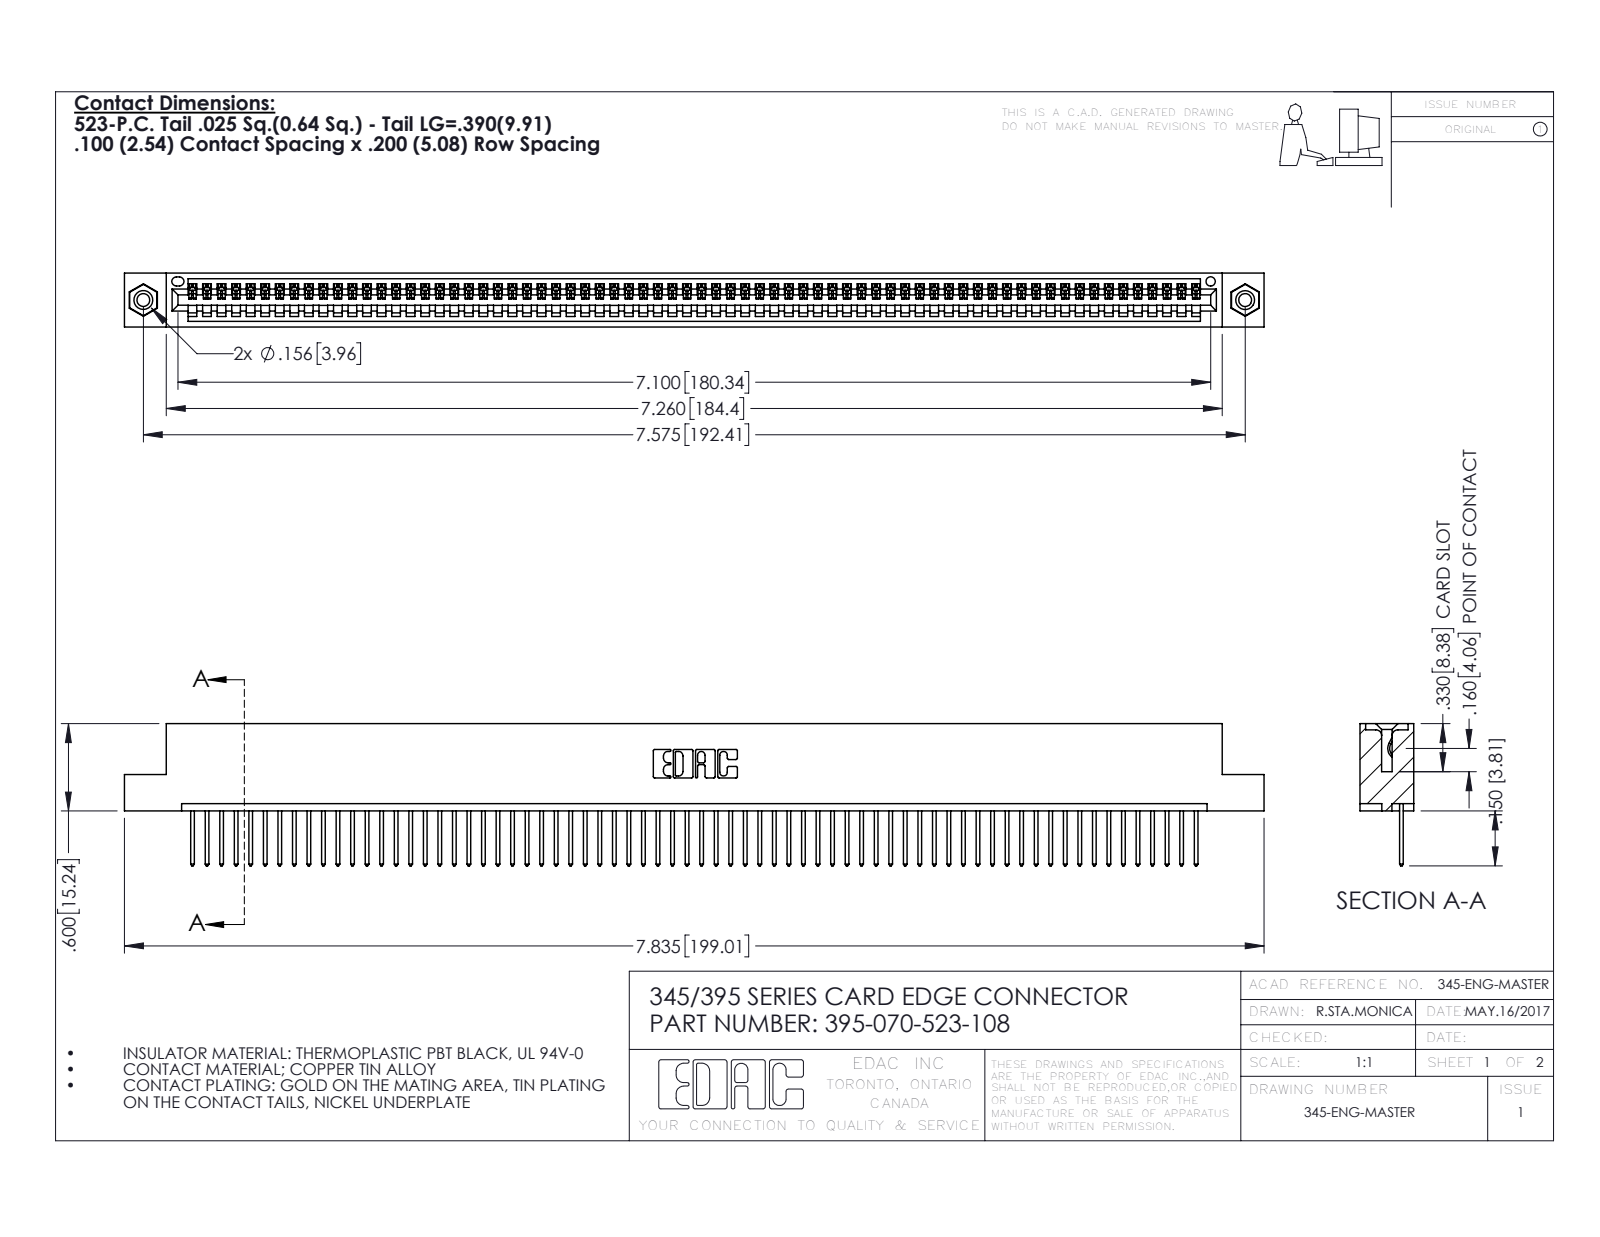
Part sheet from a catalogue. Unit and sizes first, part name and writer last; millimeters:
Units: millimetres
Overall size (bounding box): 199 × 24.8 × 9.4
Round holes (diameter × count): ⌀2.3 ×2, ⌀3.2 ×2, ⌀4 ×2, ⌀1.6 ×1
Round bosses / shafts (diameter × count): ⌀3.9 ×2
Partial cylindrical surfaces — rounded edges, fillets, slot ends (radius × count): R0.2 ×140, R0.3 ×140, R0.3 ×22, R0.2 ×6, R0.8 ×6, R0.7 ×3, R0.8 ×2, R1 ×2
Main face-to-face distances: 1.8, 7.6, 9.4, 5.1, 2.5, 6.9, 0.6, 5.7, 3.8, 1.8
Hole centre spacings: 6.9, 186.4, 192.4
Volume: 19 090 mm³ · Surface area: 25 860 mm²
Bodies: 73 solids, 4246 faces (2912 planar, 1318 cylindrical, 16 other)
Part name (STEP PRODUCT): 345 Part_Flush Mounting Lugs - 0.156 Dia-TI; 345-250-001_345-250-003-102; 345-292-001_345-293-123; 395-070-523-108
STEP written by: SolidWorks 2016 (CONFIG_CONTROL_DESIGN)
